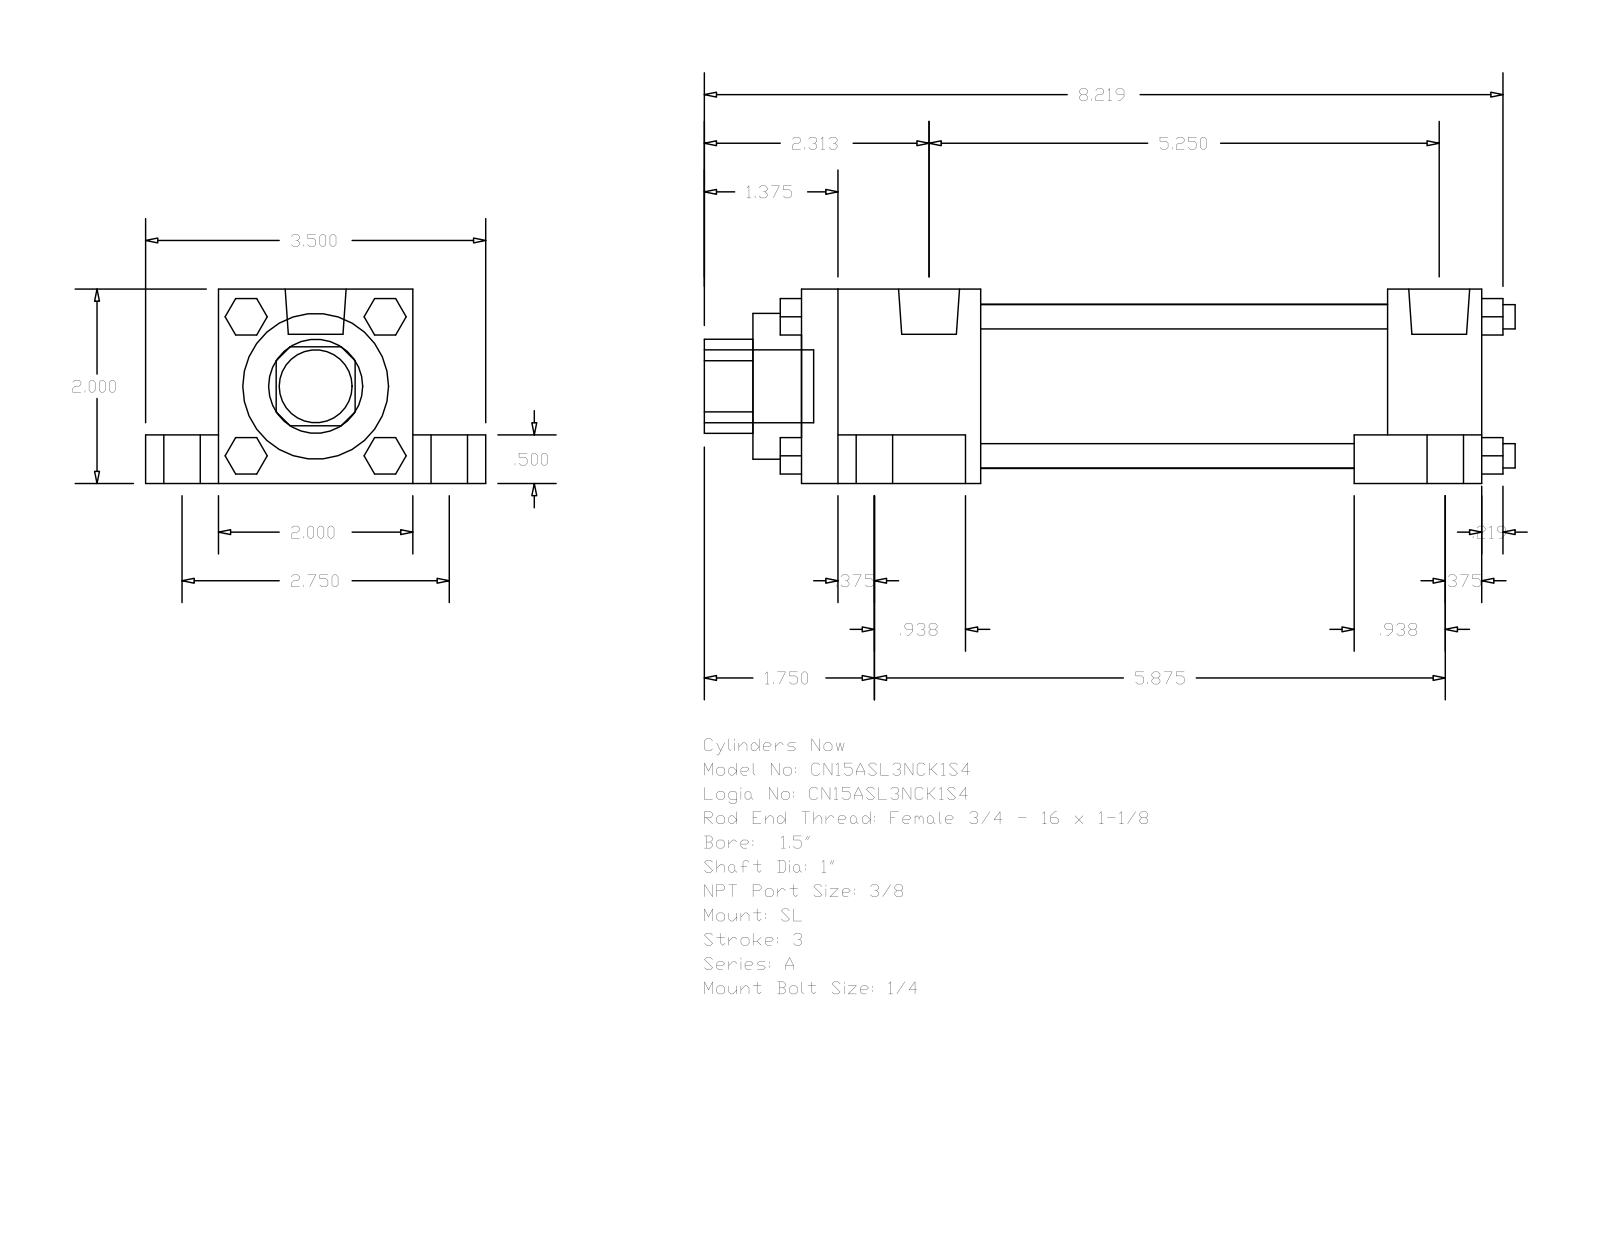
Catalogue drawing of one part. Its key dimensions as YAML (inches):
part_name: "A_SL__0150_1"
step_written_by: "GSSL Pune (CONFIG_CONTROL_DESIGN)"
units: inches
bodies: {solids: 0, faces: 148, planar: 112, cylindrical: 36, other: 0}
overall_size: [8.344, 3.5, 2]
round_holes:
  - {diameter: 1, count: 1}
  - {diameter: 1.5, count: 1}
  - {diameter: 1.69, count: 1}
round_bosses_or_shafts:
  - {diameter: 0.625, count: 4}
  - {diameter: 0.375, count: 4}
  - {diameter: 0.25, count: 4}
  - {diameter: 0.219, count: 4}
  - {diameter: 0.627, count: 2}
  - {diameter: 0.75, count: 1}
partial_cylinders:
  - {radius: 0.484, count: 1}
face_to_face_distances: [2, 0.5, 1.5, 0.75, 2.75, 0.375, 7, 1.313, 6.031, 0.969]
